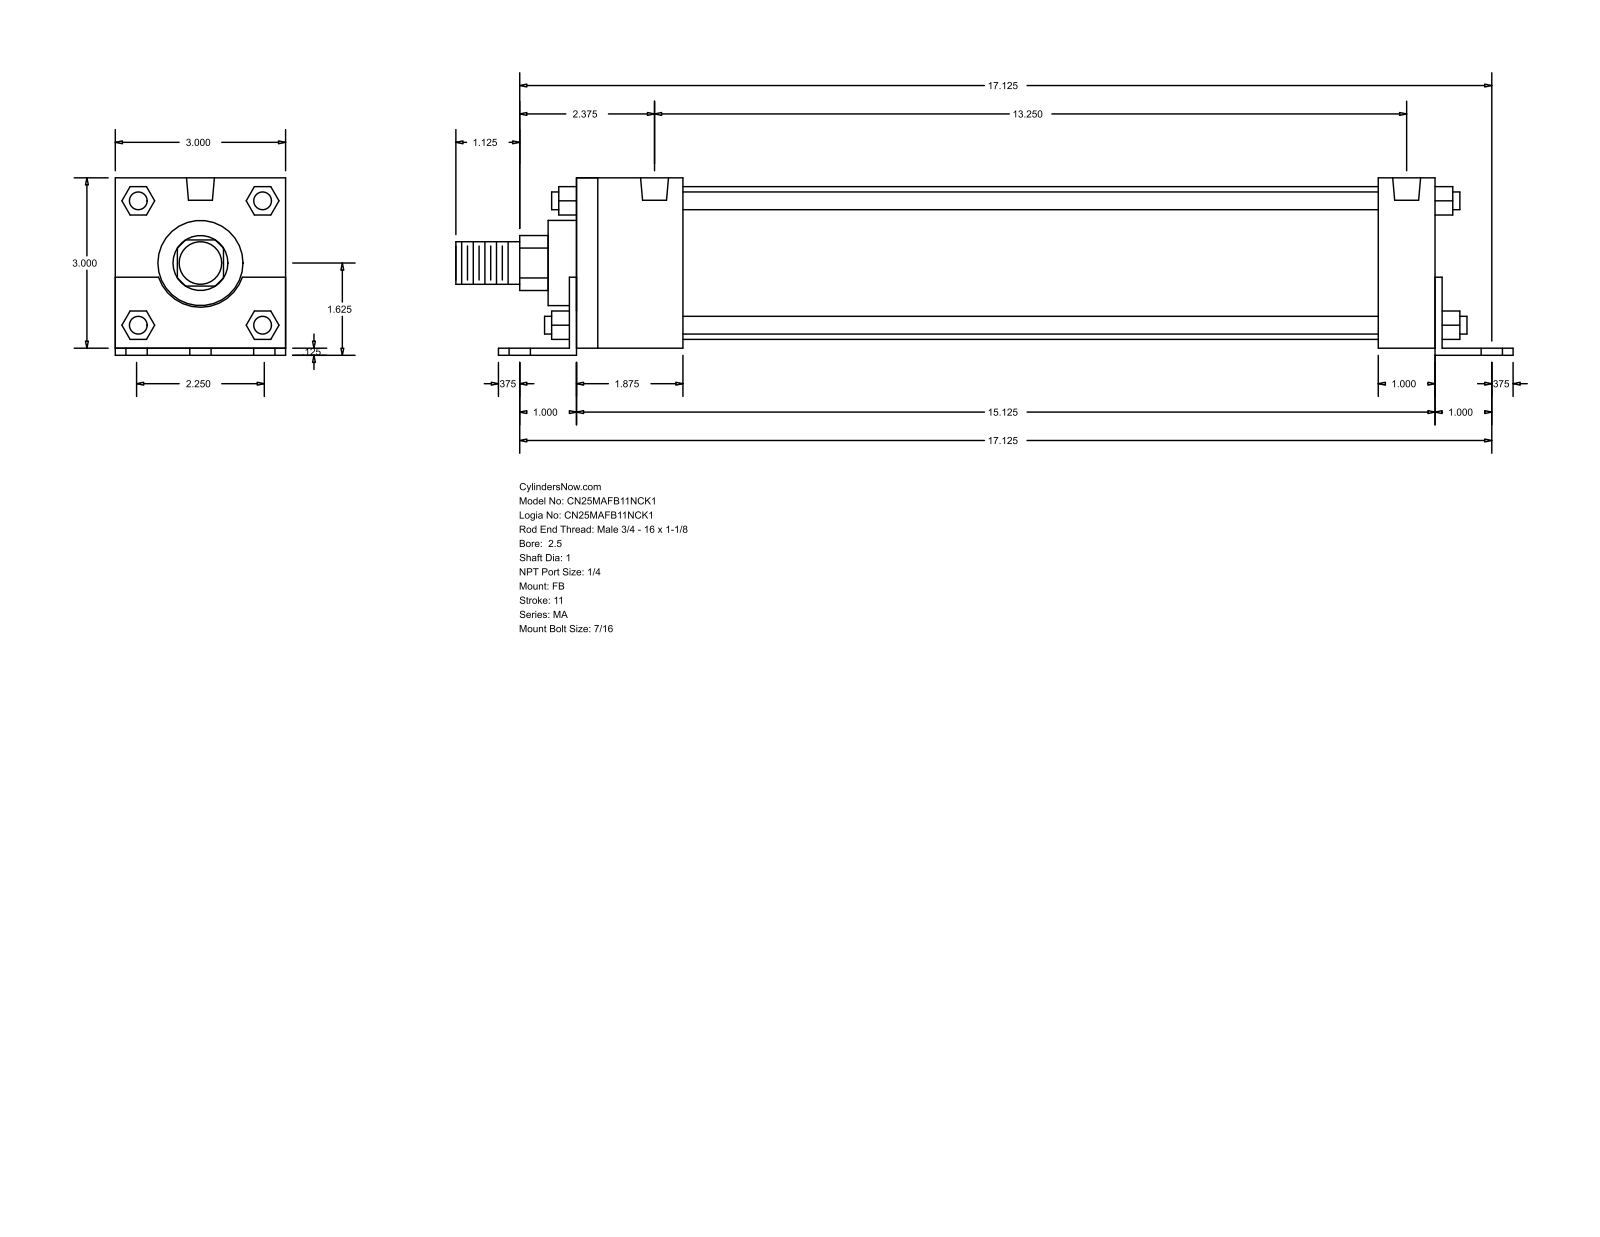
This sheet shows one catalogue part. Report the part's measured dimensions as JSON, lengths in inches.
{"part_name": "MA_FB__0250_1", "step_written_by": "GSSL Pune (CONFIG_CONTROL_DESIGN)", "units": "inches", "bodies": {"solids": 0, "faces": 140, "planar": 105, "cylindrical": 35, "other": 0}, "overall_size": [18.625, 3.125, 3], "round_holes": [[0.437, 6], [0.313, 4], [0.492, 2]], "round_bosses_or_shafts": [[0.313, 4], [2.69, 1], [1.5, 1], [1, 1], [0.75, 1]], "partial_cylinders_radius": [[0.484, 1], [0.78, 1]], "face_to_face_distances": [3, 0.125, 3.125, 15.125, 0.125, 0.5, 15.25, 1.125, 2, 1.875], "hole_center_spacings": [1.125, 17.162, 17.125, 1.875, 2.25, 2.628, 13.25, 14.793]}
